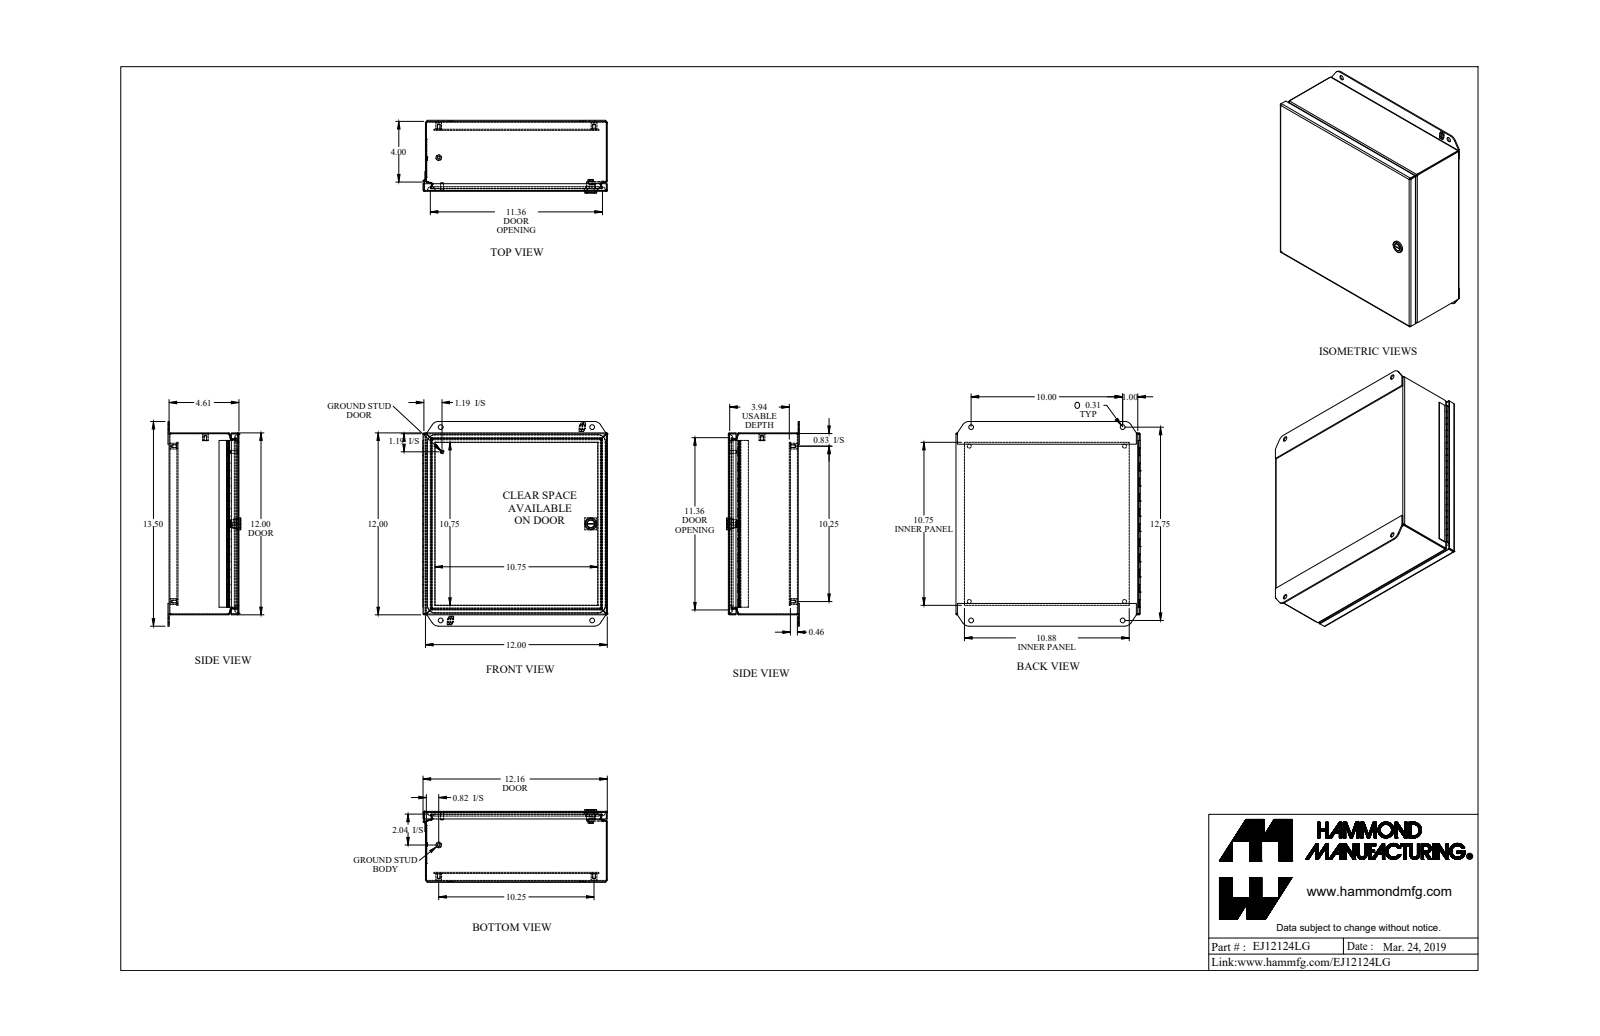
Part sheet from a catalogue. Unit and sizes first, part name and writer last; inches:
Units: inches
Overall size (bounding box): 13.5 × 12.165 × 4.805
Round holes (diameter × count): ⌀0.156 ×5, ⌀0.265 ×4, ⌀0.313 ×4, ⌀0.05 ×1, ⌀0.516 ×1
Round bosses / shafts (diameter × count): ⌀0.375 ×5, ⌀0.788 ×1, ⌀0.535 ×1, ⌀0.496 ×1, ⌀0.435 ×1, ⌀0.25 ×1, ⌀0.188 ×1, ⌀0.1 ×1
Partial cylindrical surfaces — rounded edges, fillets, slot ends (radius × count): R0.029 ×16, R0.086 ×16, R0.281 ×10, R0.25 ×4, R0.499 ×4, R0.5 ×4, R0.06 ×2, R0.539 ×2
Main face-to-face distances: 0.057, 4.554, 11.943, 0.072, 0.589, 4.611, 4.497, 0.46, 0.517, 4.094
Hole centre spacings: 10.25, 5.13, 10.202, 14.496, 15.322, 1.256, 1.256, 11.501
Volume: 46.38 in³ · Surface area: 1 519 in²
Bodies: 16 solids, 707 faces (393 planar, 222 cylindrical, 92 other)
Part name (STEP PRODUCT): EJ12124LG_Default
STEP written by: SolidWorks 2019 (CONFIG_CONTROL_DESIGN)
